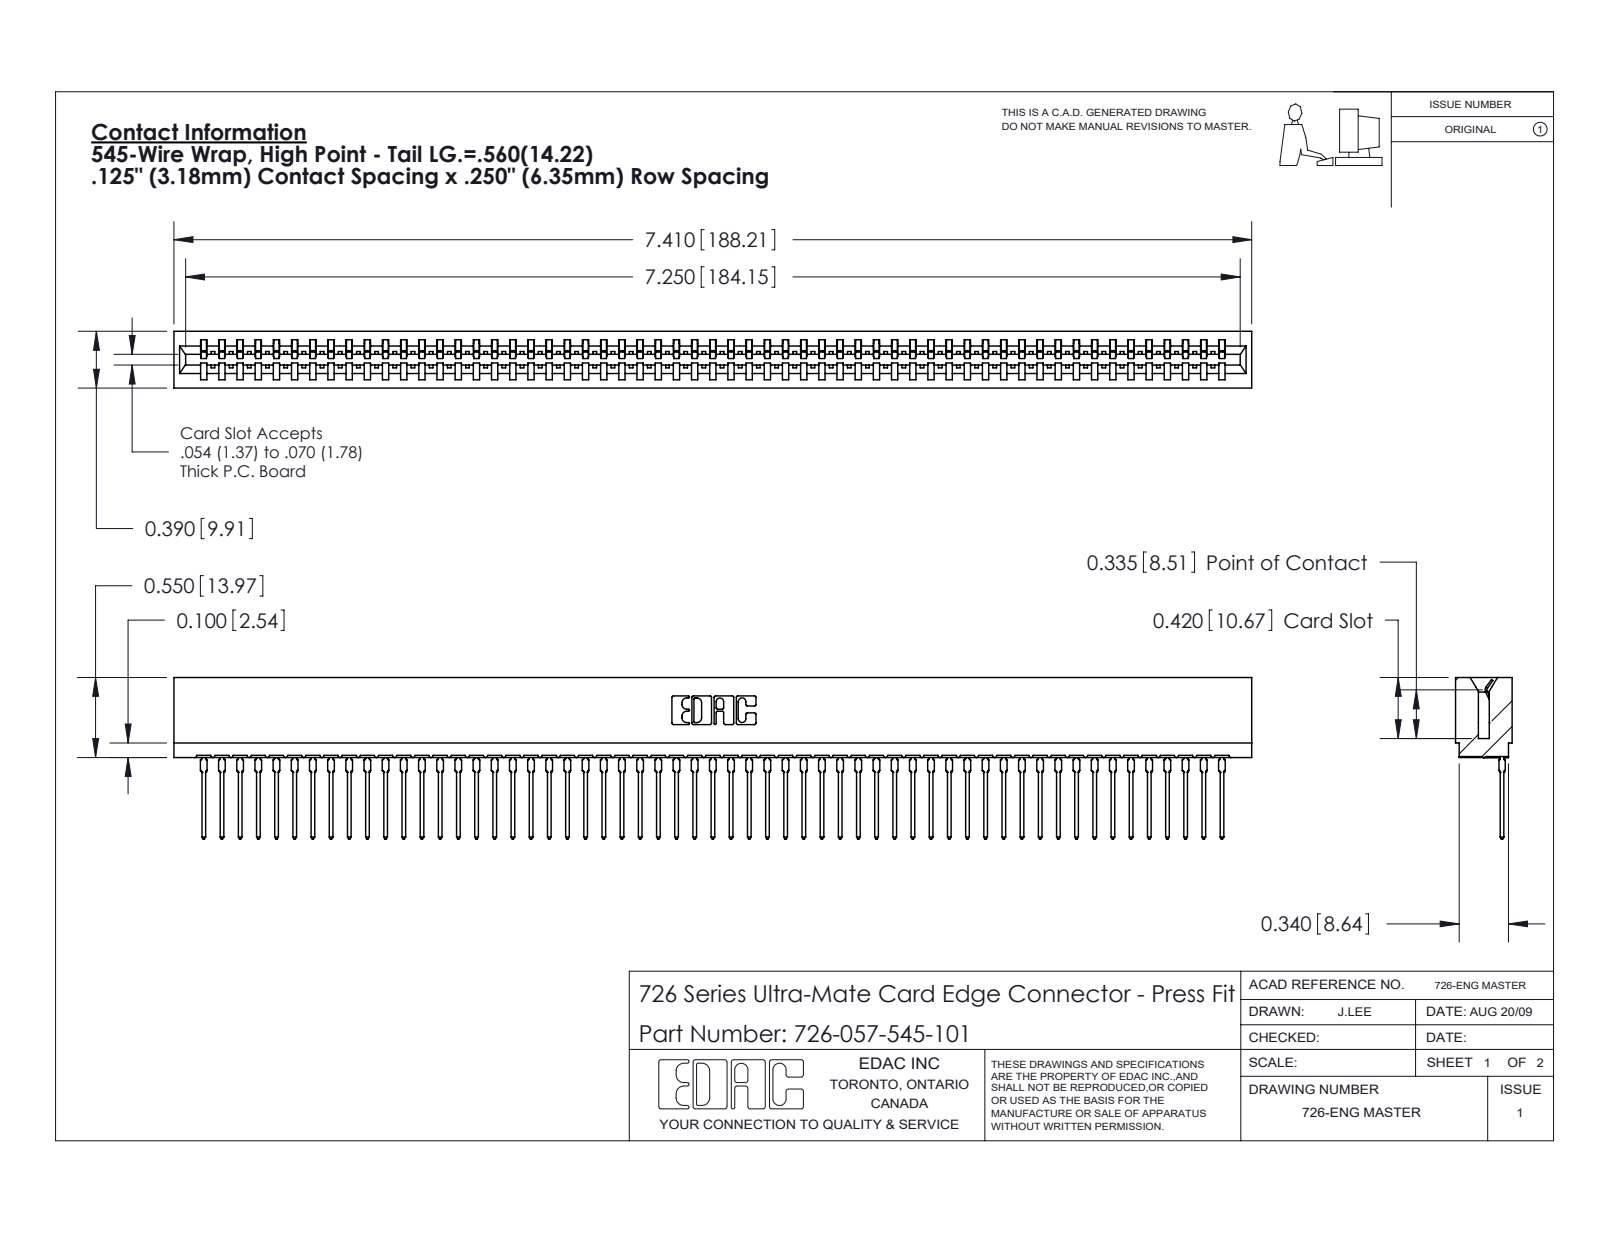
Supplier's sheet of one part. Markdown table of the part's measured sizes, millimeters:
| quantity | value |
| --- | --- |
| part name | 746-292-001_545; 726-057-545-101; 726 Part_.515 Slot Depth - 01 |
| STEP written by | SolidWorks 2020 (CONFIG_CONTROL_DESIGN) |
| units | millimeters |
| bodies | 58 solids, 6253 faces (3646 planar, 1125 cylindrical, 1482 other) |
| overall size | 188.2 × 28.2 × 9.9 |
| volume | 16 880 mm³ |
| surface area | 26 770 mm² |
| partial cylindrical surfaces (radius × count) | 0.5 × 114, 0.4 × 58, 0.3 × 22, 0.2 × 6, 0.8 × 6, 0.1 × 4, 0.3 × 4, 0.7 × 3 |
| main face-to-face distances | 1.4, 8.5, 9.9, 0.6, 7.8, 6.4, 2.1, 7, 9.3, 0.8 |
